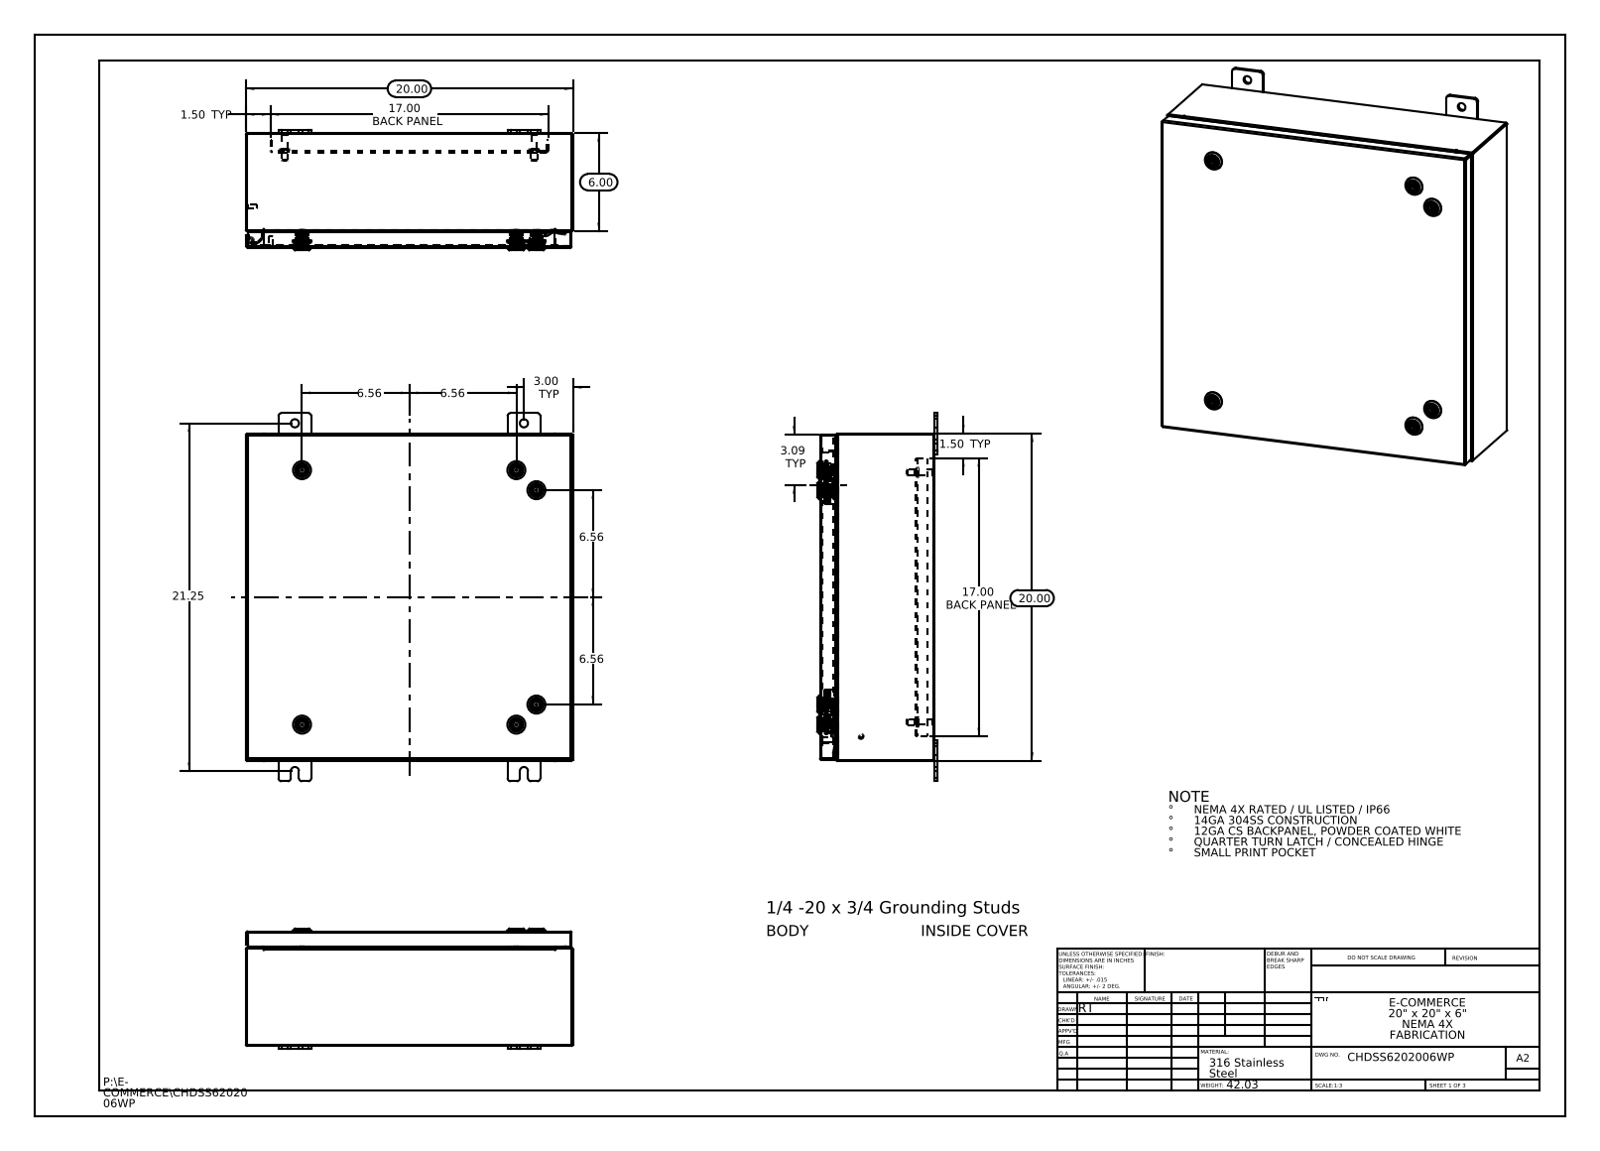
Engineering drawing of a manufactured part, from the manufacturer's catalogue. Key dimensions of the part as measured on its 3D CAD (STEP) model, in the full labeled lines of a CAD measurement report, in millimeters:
Part name (STEP PRODUCT): CHDSS6202006WP Backpanel; CHDSS6202006WP Top; HW-CLH-E5-8004_Cam-232112-U-Industrilas; CHDSS6202006WP Body (+8 more)
STEP written by: SolidWorks 2013 (CONFIG_CONTROL_DESIGN)
Units: millimetres
Bodies: 55 solids, 5420 faces (1592 planar, 1692 cylindrical, 2136 other)
Overall size (bounding box): 571.5 × 508 × 186.8
Volume: 2 481 000 mm³ · Surface area: 2 432 000 mm²
Round holes (diameter × count): ⌀12.7 ×8, ⌀5 ×6, ⌀10 ×6, ⌀10.2 ×6, ⌀16 ×6, ⌀20 ×6, ⌀3.5 ×4, ⌀5.4 ×1
Round bosses / shafts (diameter × count): ⌀6 ×8, ⌀28 ×6, ⌀19.8 ×6, ⌀15.9 ×6, ⌀15.5 ×6, ⌀13.5 ×6, ⌀10 ×6, ⌀2.9 ×6
Partial cylindrical surfaces — rounded edges, fillets, slot ends (radius × count): R0.2 ×198, R3 ×198, R0.7 ×72, R0.5 ×24, R4.8 ×24, R5 ×24, R0.3 ×20, R2.2 ×18
Main face-to-face distances: 1.9, 1.9, 506.1, 178.1, 176.1, 176.2, 174.3, 2.6, 25.4, 27.3
Hole centre spacings: 332.7, 365.2, 17.5, 47.2, 77.9, 347.6, 355.6, 359.8
